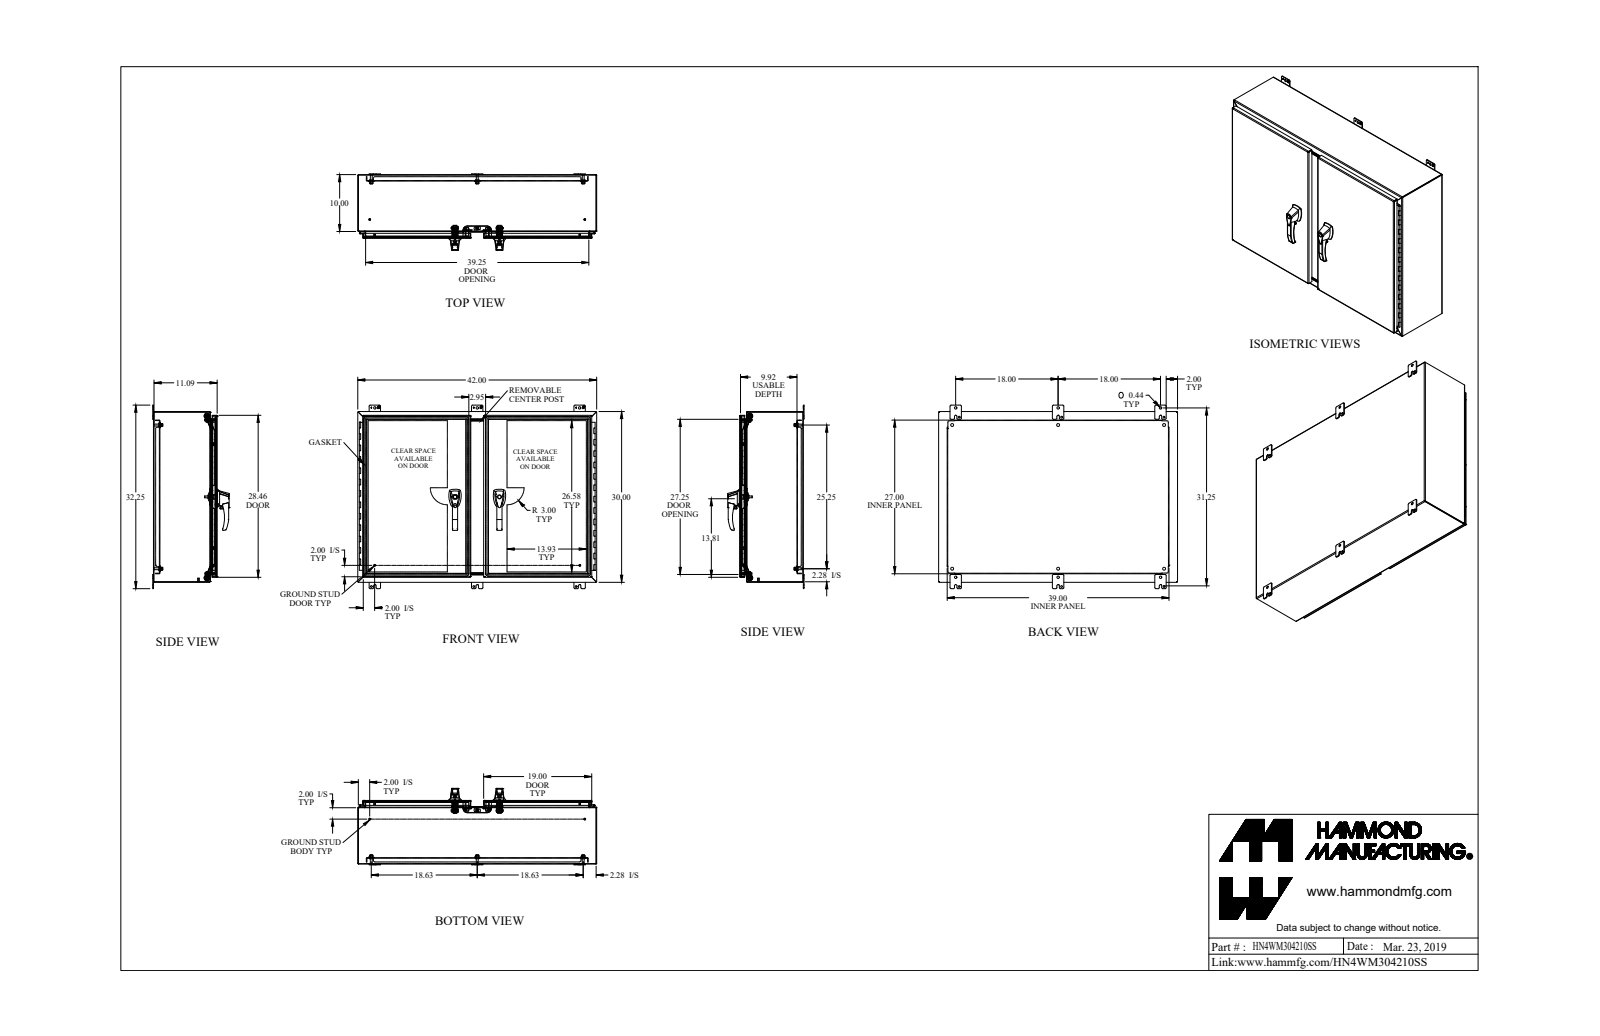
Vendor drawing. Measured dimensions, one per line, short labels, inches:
name: HN4WM304210SS
written by: SolidWorks 2018 (AUTOMOTIVE_DESIGN)
unit: in
bodies: 108 solids, 2772 faces (1305 planar, 1187 cylindrical, 280 other)
size: 42 × 32.25 × 13.425
volume: 602.2 in³; area: 12 450 in²
holes: 10× ⌀0.304, 9× ⌀0.313, 8× ⌀0.25, 6× ⌀0.201, 6× ⌀0.307, 6× ⌀0.445, 6× ⌀0.5, 4× ⌀0.281, 4× ⌀0.313, 4× ⌀0.39, 3× ⌀0.437, 2× ⌀0.11
bosses: 8× ⌀1, 6× ⌀0.65, 6× ⌀0.375, 6× ⌀0.332, 6× ⌀0.293, 4× ⌀0.75, 4× ⌀0.625, 4× ⌀0.44
rounds: 37× R0.125, 34× R0.25, 32× R0.018, 26× R0.188, 22× R0.06, 21× R0.5, 19× R0.048, 19× R0.143
face distances: 0.095, 1.032, 0.095, 11.09, 10.995, 0.937, 11.185, 11.09, 9.963, 1.127
hole spacings: 31.376, 6, 40.588, 18.625, 12, 25.25, 37.25, 41.897
